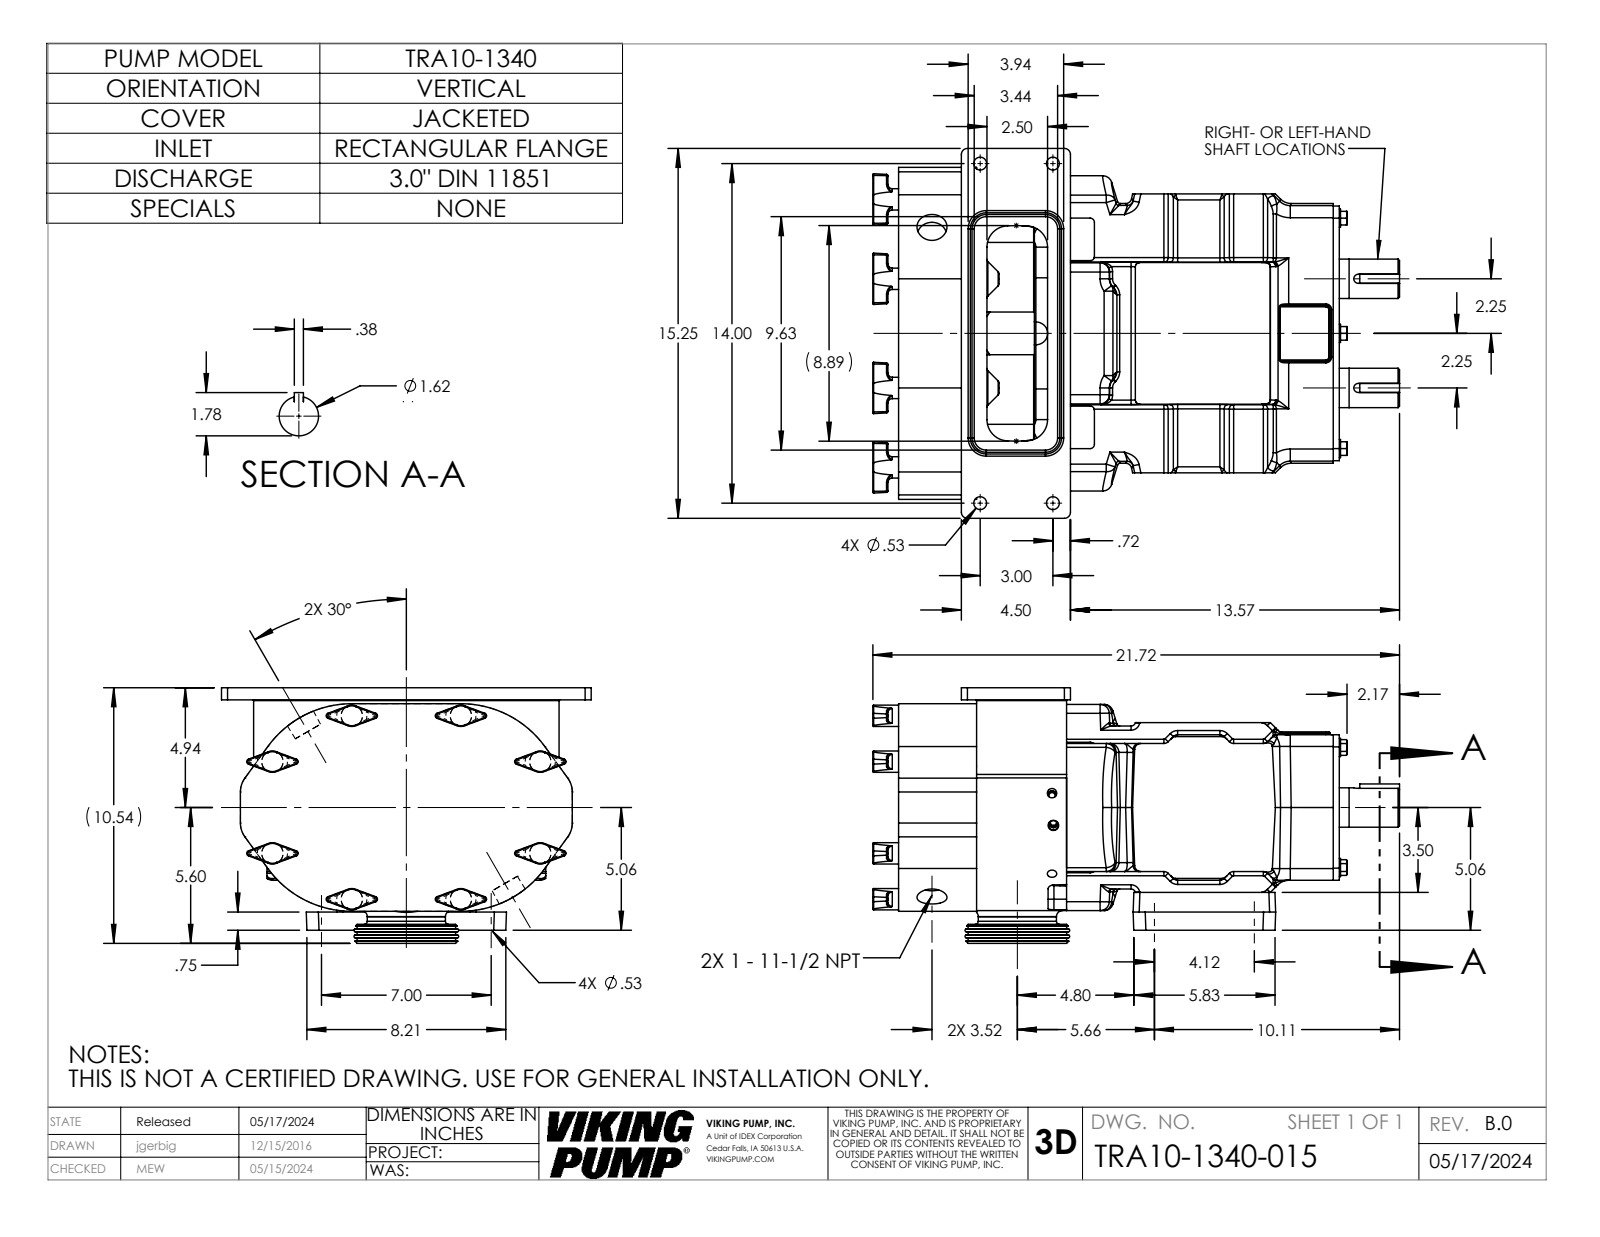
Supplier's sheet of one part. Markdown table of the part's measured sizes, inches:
| quantity | value |
| --- | --- |
| part name | 1300DIN11851-30; TRA10-0600-GEARBOX-V; TRA10-0600-COVER-JACKET; WT1340BDY (+3 more) |
| STEP written by | SolidWorks 2023 (AUTOMOTIVE_DESIGN) |
| units | inches |
| bodies | 4 solids, 1413 faces (331 planar, 500 cylindrical, 582 other) |
| overall size | 21.724 × 15.25 × 10.539 |
| volume | 1 322 in³ |
| surface area | 1 777 in² |
| round holes (diameter × count) | 0.437 × 8, 0.531 × 8, 0.25 × 4, 0.332 × 3, 0.187 × 2, 0.313 × 2, 0.625 × 2, 2.237 × 2, 2.315 × 2, 2.613 × 2, 3.5 × 2, 4.41 × 2 |
| round bosses / shafts (diameter × count) | 0.88 × 8, 0.75 × 6, 2.999 × 2, 1.624 × 2, 3.346 × 1, 3.224 × 1 |
| partial cylindrical surfaces (radius × count) | 0.18 × 44, 0.06 × 43, 0.25 × 41, 0.03 × 36, 0.38 × 28, 0.5 × 27, 0.12 × 24, 0.09 × 16 |
| main face-to-face distances | 3.218, 6.93, 3.711, 0.5, 0.36, 18.18, 14.961, 11.25, 1.437, 5.64 |
| hole center spacings | 3.781, 1.949, 3.781, 4.013, 5.325, 5.878, 6.961, 8.002 |
